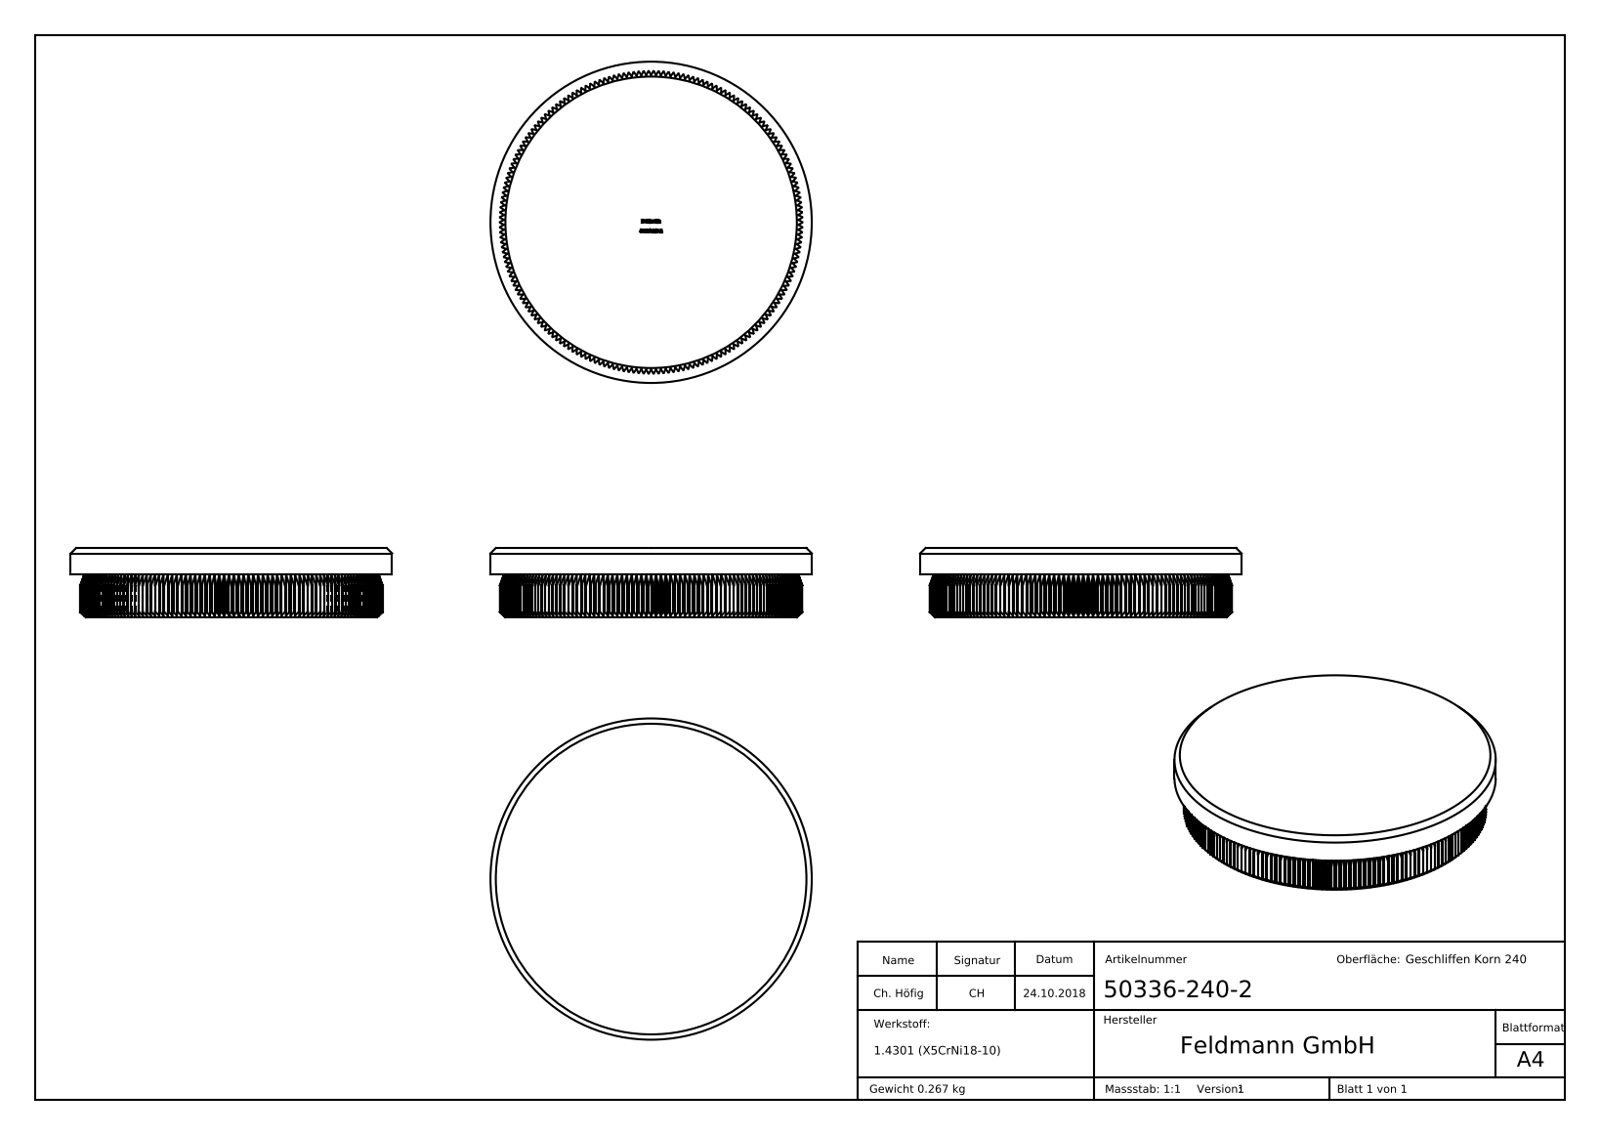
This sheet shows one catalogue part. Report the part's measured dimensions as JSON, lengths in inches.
{"part_name": "50336-240-2", "step_written_by": "SolidWorks 2015 (CONFIG_CONTROL_DESIGN)", "units": "inches", "bodies": {"solids": 1, "faces": 1020, "planar": 511, "cylindrical": 192, "other": 317}, "overall_size": [2.374, 2.374, 0.512], "volume_in3": 2.066, "surface_area_in2": 13.87, "round_bosses_or_shafts": [[2.374, 1]], "partial_cylinders_radius": [[1.116, 1]], "face_to_face_distances": [0.512, 0.315, 0.197, 1.088, 1.089, 1.087, 1.09, 0.311, 0.508, 0.07]}
